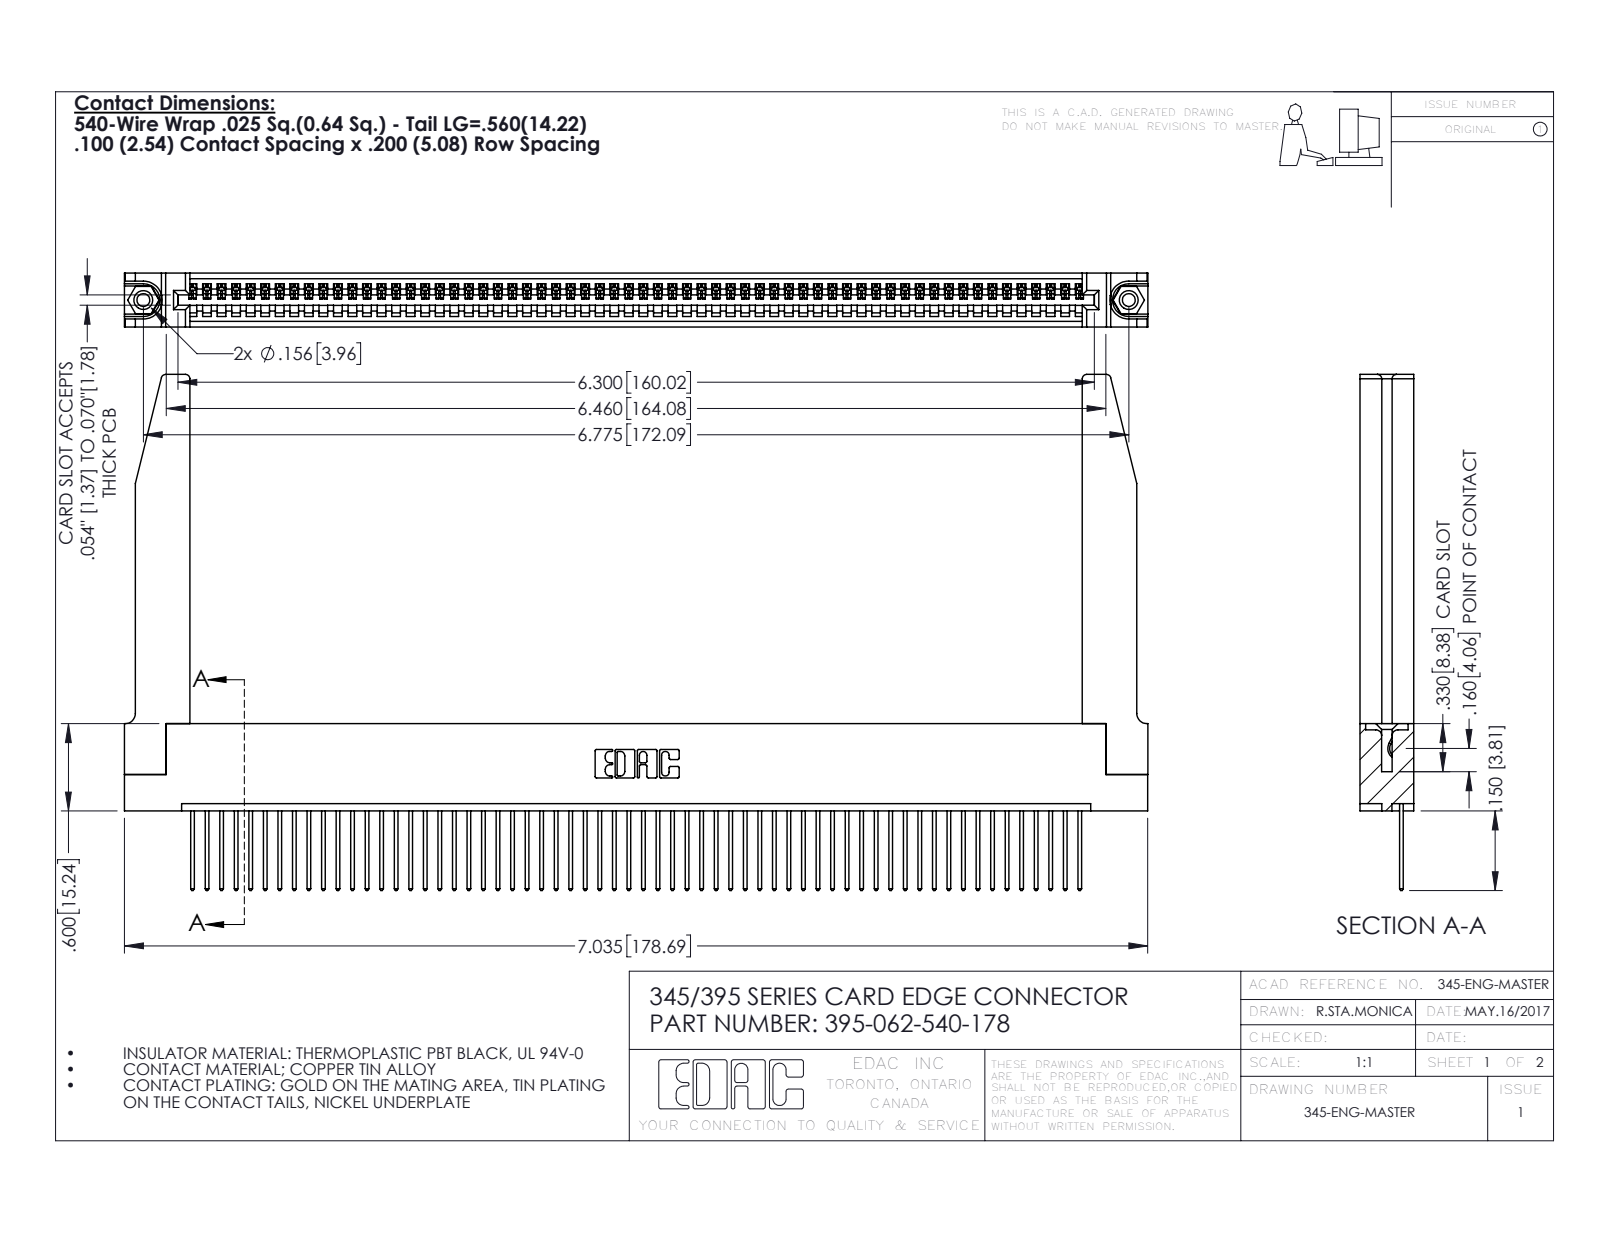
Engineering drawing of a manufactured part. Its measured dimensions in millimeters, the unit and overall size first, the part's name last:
Units: millimetres
Overall size (bounding box): 178.7 × 90.1 × 9.4
Round holes (diameter × count): ⌀2.3 ×2, ⌀3.2 ×2, ⌀4 ×2, ⌀1.6 ×1
Round bosses / shafts (diameter × count): ⌀3.9 ×2
Partial cylindrical surfaces — rounded edges, fillets, slot ends (radius × count): R0.2 ×124, R0.3 ×124, R0.3 ×22, R0.8 ×8, R0.2 ×6, R0.8 ×6, R0.7 ×3, R0.8 ×2
Main face-to-face distances: 1.8, 7.6, 9.4, 2.5, 6.9, 0.6, 5.1, 5.7, 3.8, 3.8
Hole centre spacings: 6.9, 166.1, 172.1
Volume: 24 990 mm³ · Surface area: 30 610 mm²
Bodies: 67 solids, 3956 faces (2702 planar, 1202 cylindrical, 52 other)
Part name (STEP PRODUCT): 345 Part_Flush Mounting Lugs - 0.156 Dia-TH; 345-220-078_345-220-078; 345-250-001_345-250-001-102; 395-062-540-178 (+1 more)
STEP written by: SolidWorks 2016 (CONFIG_CONTROL_DESIGN)
